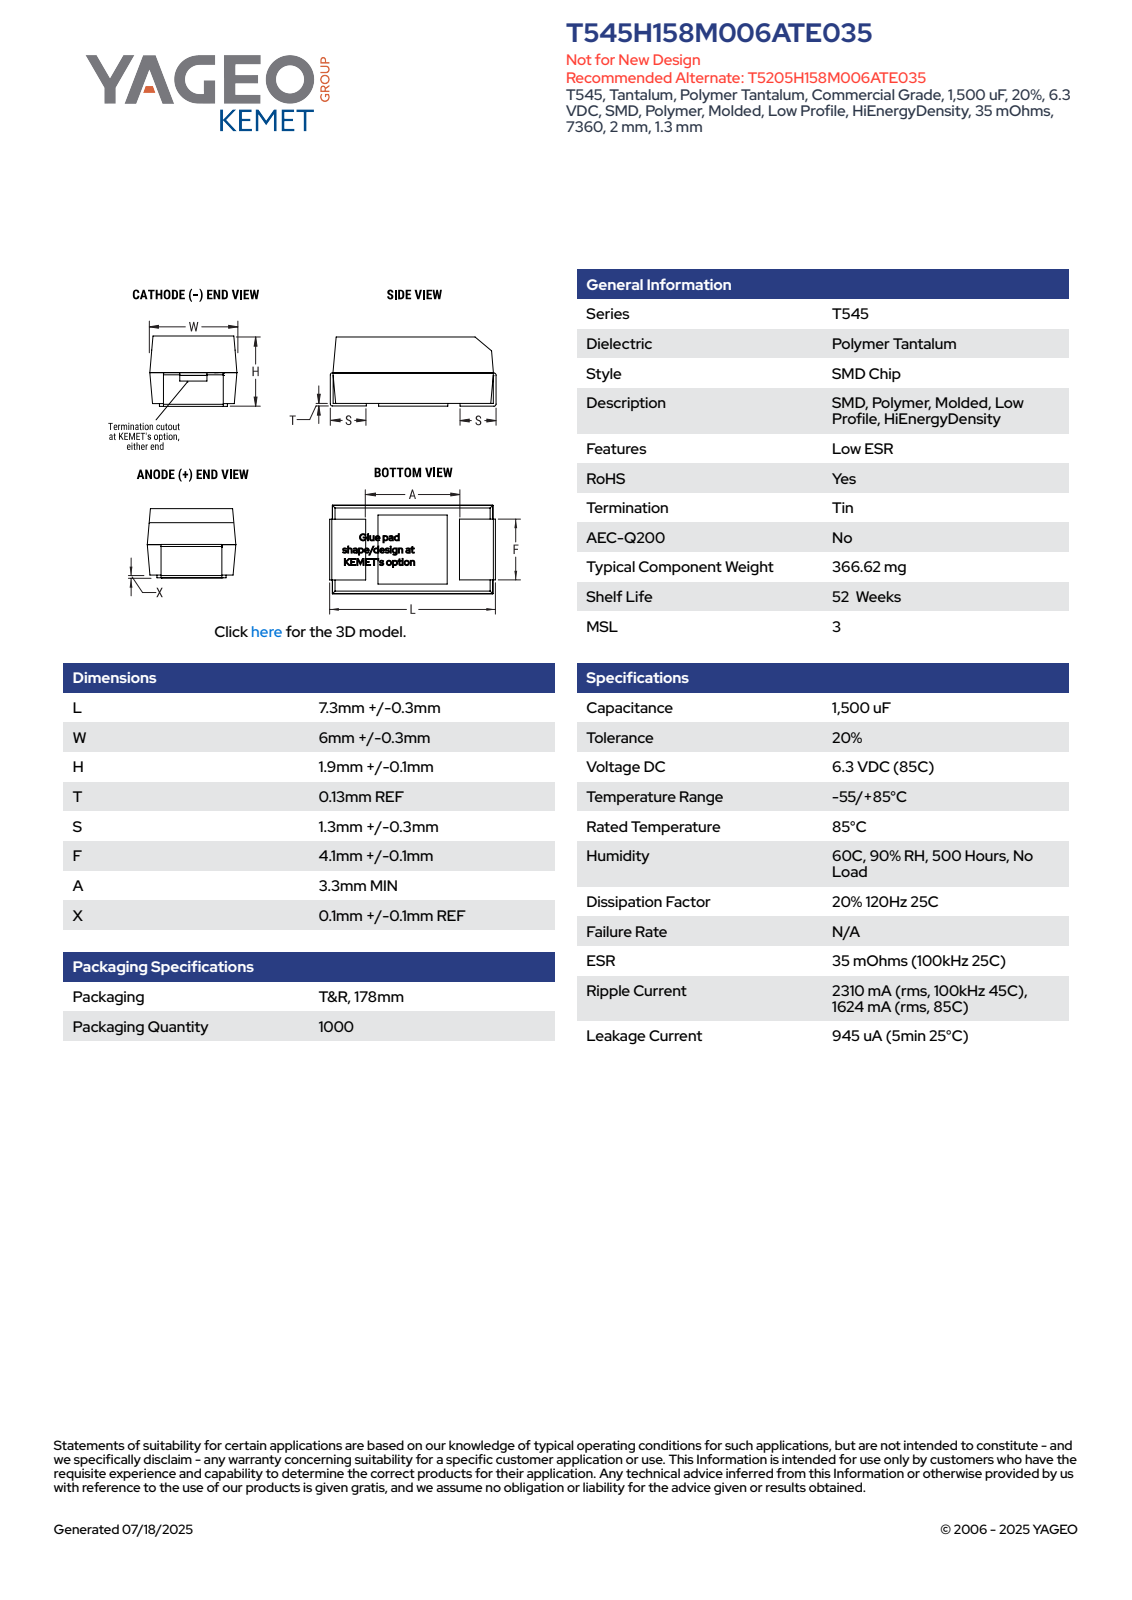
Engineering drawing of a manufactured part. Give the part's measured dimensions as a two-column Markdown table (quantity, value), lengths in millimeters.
| quantity | value |
| --- | --- |
| part name | Case_Top_26; Case_Cathode_26; Case_Bottom_26; CTS7360H_L7.6W6.3H2S1.3F4.1 (+1 more) |
| STEP written by | SolidWorks 2014 (AUTOMOTIVE_DESIGN) |
| units | millimeters |
| bodies | 7 solids, 94 faces (90 planar, 4 cylindrical, 0 other) |
| overall size | 7.6 × 6.3 × 2 |
| volume | 88 mm³ |
| surface area | 275 mm² |
| main face-to-face distances | 1.02, 0.85, 1.87, 0.95, 1.97, 6.28, 7.31, 2, 0.98, 7.47 |
